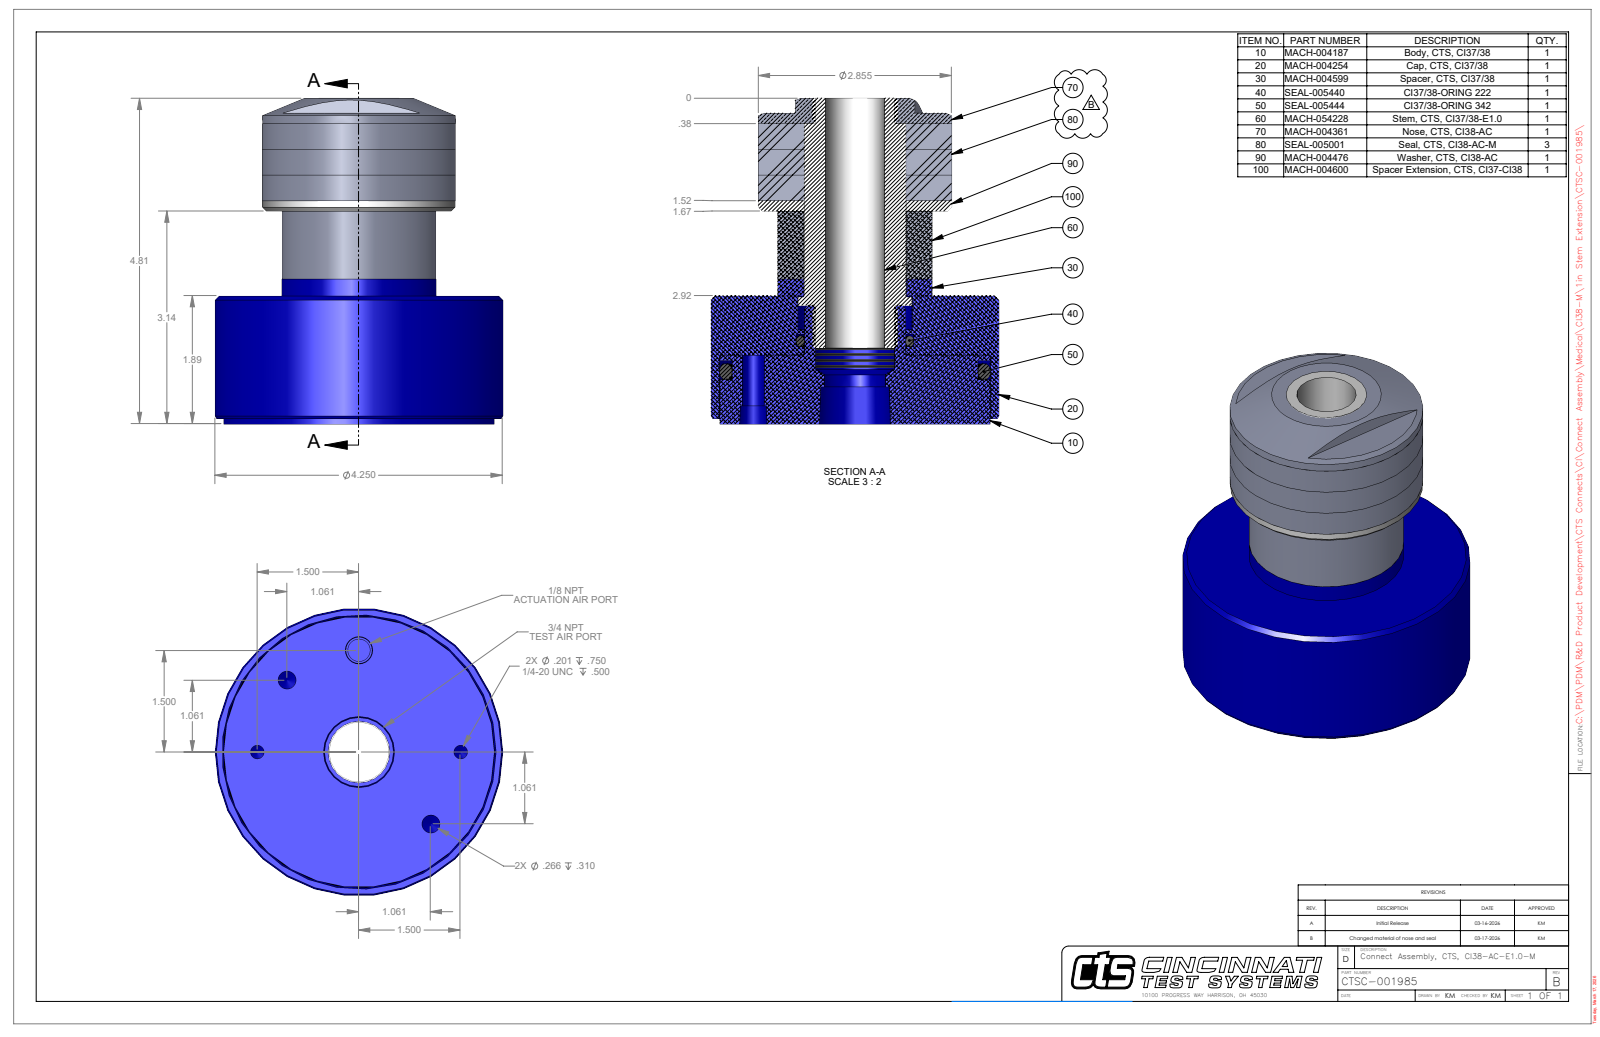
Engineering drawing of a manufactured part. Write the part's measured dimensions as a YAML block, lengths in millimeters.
part_name: "CTSC-001985"
step_written_by: "SolidWorks 2023 (AUTOMOTIVE_DESIGN)"
units: millimeters
bodies: {solids: 8, faces: 77, planar: 37, cylindrical: 28, other: 12}
overall_size: [122.25, 107.95, 107.95]
volume: 629321
surface_area: 114283
round_holes:
  - {diameter: 5.11, count: 2}
  - {diameter: 6.75, count: 2}
  - {diameter: 22.35, count: 1}
  - {diameter: 23.01, count: 1}
  - {diameter: 29.77, count: 1}
  - {diameter: 37.97, count: 1}
  - {diameter: 37.97, count: 1}
  - {diameter: 38.35, count: 1}
  - {diameter: 42.88, count: 1}
  - {diameter: 101.6, count: 1}
round_bosses_or_shafts:
  - {diameter: 107.95, count: 1}
  - {diameter: 101.4, count: 1}
  - {diameter: 72.52, count: 1}
  - {diameter: 72.52, count: 1}
  - {diameter: 57.94, count: 1}
  - {diameter: 42.52, count: 1}
  - {diameter: 38.05, count: 1}
  - {diameter: 31.75, count: 1}
face_to_face_distances: [9.65, 19.31, 48.08, 112.65, 64.57, 103, 54.92, 93.34, 45.26, 9.66]
hole_center_spacings: [38.1, 29.16, 70.4, 76.2]
